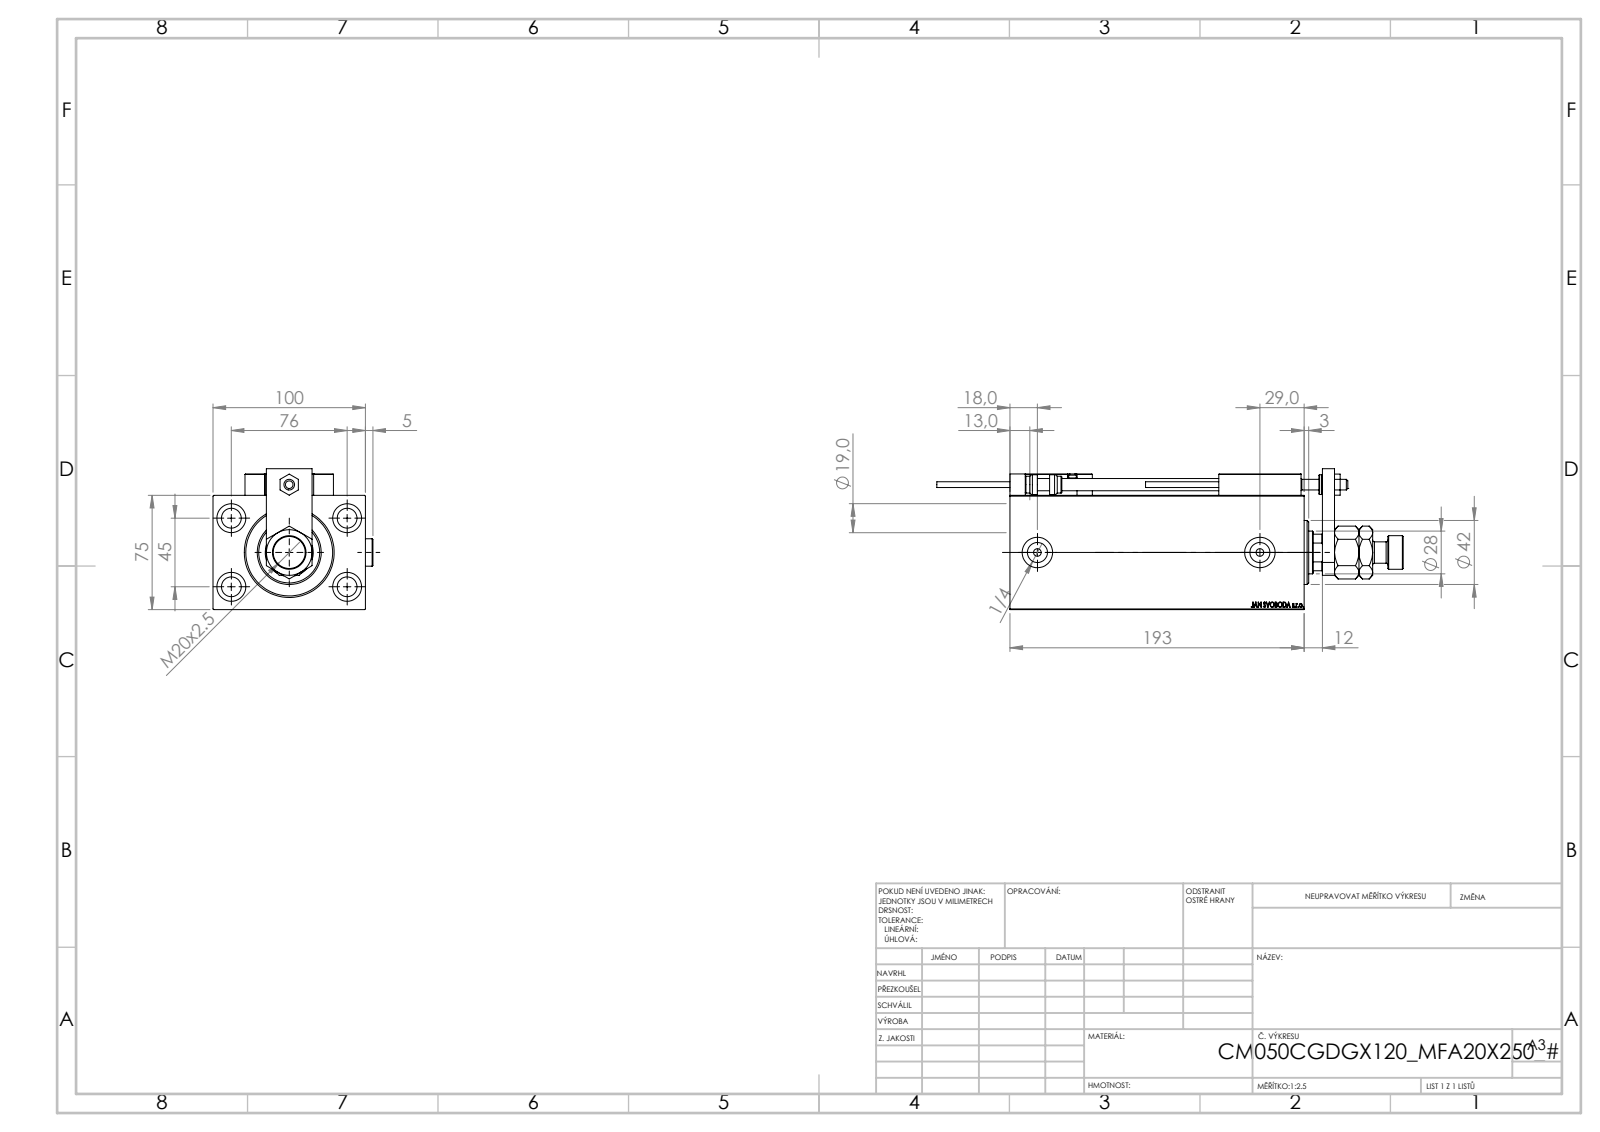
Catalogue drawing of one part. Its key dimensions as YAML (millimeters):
part_name: "MAGNET; ZARAZKA; KONCOVKA; V450CM_VC_B (+7 more)"
step_written_by: "SolidWorks 2019 (CONFIG_CONTROL_DESIGN)"
units: millimeters
bodies: {solids: 26, faces: 1391, planar: 611, cylindrical: 210, other: 570}
overall_size: [306, 104.9, 92.5]
volume: 1248000
surface_area: 215145
round_holes:
  - {diameter: 8, count: 5}
  - {diameter: 3.2, count: 4}
  - {diameter: 4, count: 4}
  - {diameter: 5, count: 4}
  - {diameter: 13, count: 4}
  - {diameter: 19, count: 4}
  - {diameter: 20, count: 3}
  - {diameter: 13.16, count: 2}
  - {diameter: 7, count: 1}
  - {diameter: 18.5, count: 1}
  - {diameter: 28, count: 1}
  - {diameter: 31.5, count: 1}
round_bosses_or_shafts:
  - {diameter: 18, count: 2}
  - {diameter: 5, count: 2}
  - {diameter: 3.8, count: 2}
  - {diameter: 42, count: 1}
  - {diameter: 22, count: 1}
  - {diameter: 14, count: 1}
  - {diameter: 13, count: 1}
  - {diameter: 11, count: 1}
partial_cylinders:
  - {radius: 0.3, count: 30}
  - {radius: 3, count: 2}
  - {radius: 13.5, count: 1}
face_to_face_distances: [75, 100, 14, 193, 12, 179, 20, 8, 24, 25]
hole_center_spacings: [44.16, 11.37, 20, 29.59, 29.69, 36.06, 42.19, 43.91]
